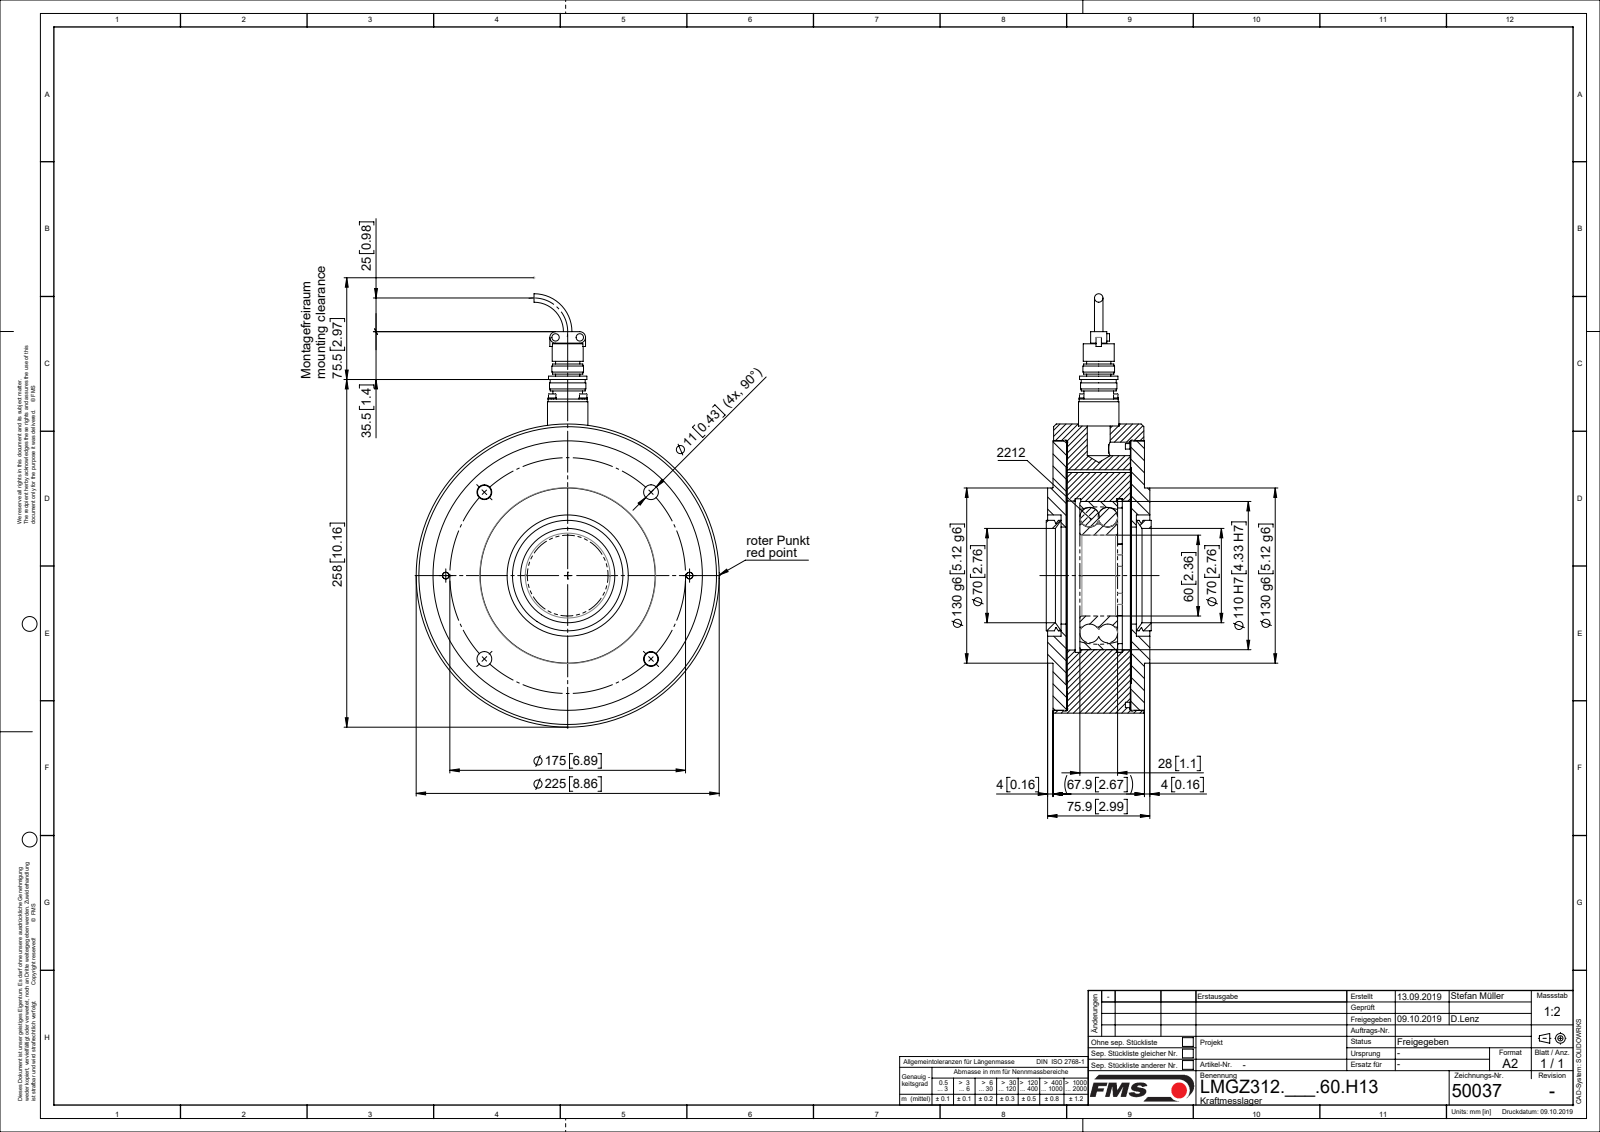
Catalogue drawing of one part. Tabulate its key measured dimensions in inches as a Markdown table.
| quantity | value |
| --- | --- |
| part name | L50037; L4765504; TEIL1; L49026 (+8 more) |
| STEP written by | Mechanical Desktop 2007 (CONFIG_CONTROL_DESIGN) |
| units | inches |
| bodies | 21 solids, 418 faces (114 planar, 240 cylindrical, 64 other) |
| overall size | 12.663 × 8.858 × 3.067 |
| volume | 145.1 in³ |
| surface area | 610.7 in² |
| round holes (diameter × count) | 0.433 × 6, 0.102 × 4, 0.126 × 4, 0.134 × 4, 0.354 × 4, 0.197 × 2, 0.26 × 2, 0.906 × 1, 2.362 × 1, 2.756 × 1, 2.835 × 1, 3.472 × 1 |
| round bosses / shafts (diameter × count) | 0.217 × 6, 0.244 × 4, 0.118 × 4, 0.098 × 4, 0.394 × 2, 0.236 × 2, 8.858 × 1, 7.835 × 1 |
| partial cylindrical surfaces (radius × count) | 0.167 × 2, 3.189 × 1, 3.386 × 1 |
| main face-to-face distances | 1.86, 0.411, 0.402, 2.262, 2.272, 1.87, 0.02, 1.89, 0.382, 2.291 |
| hole center spacings | 0.64, 0.906, 2.684, 3.445, 4.872, 6.474, 1.281, 3.563 |
